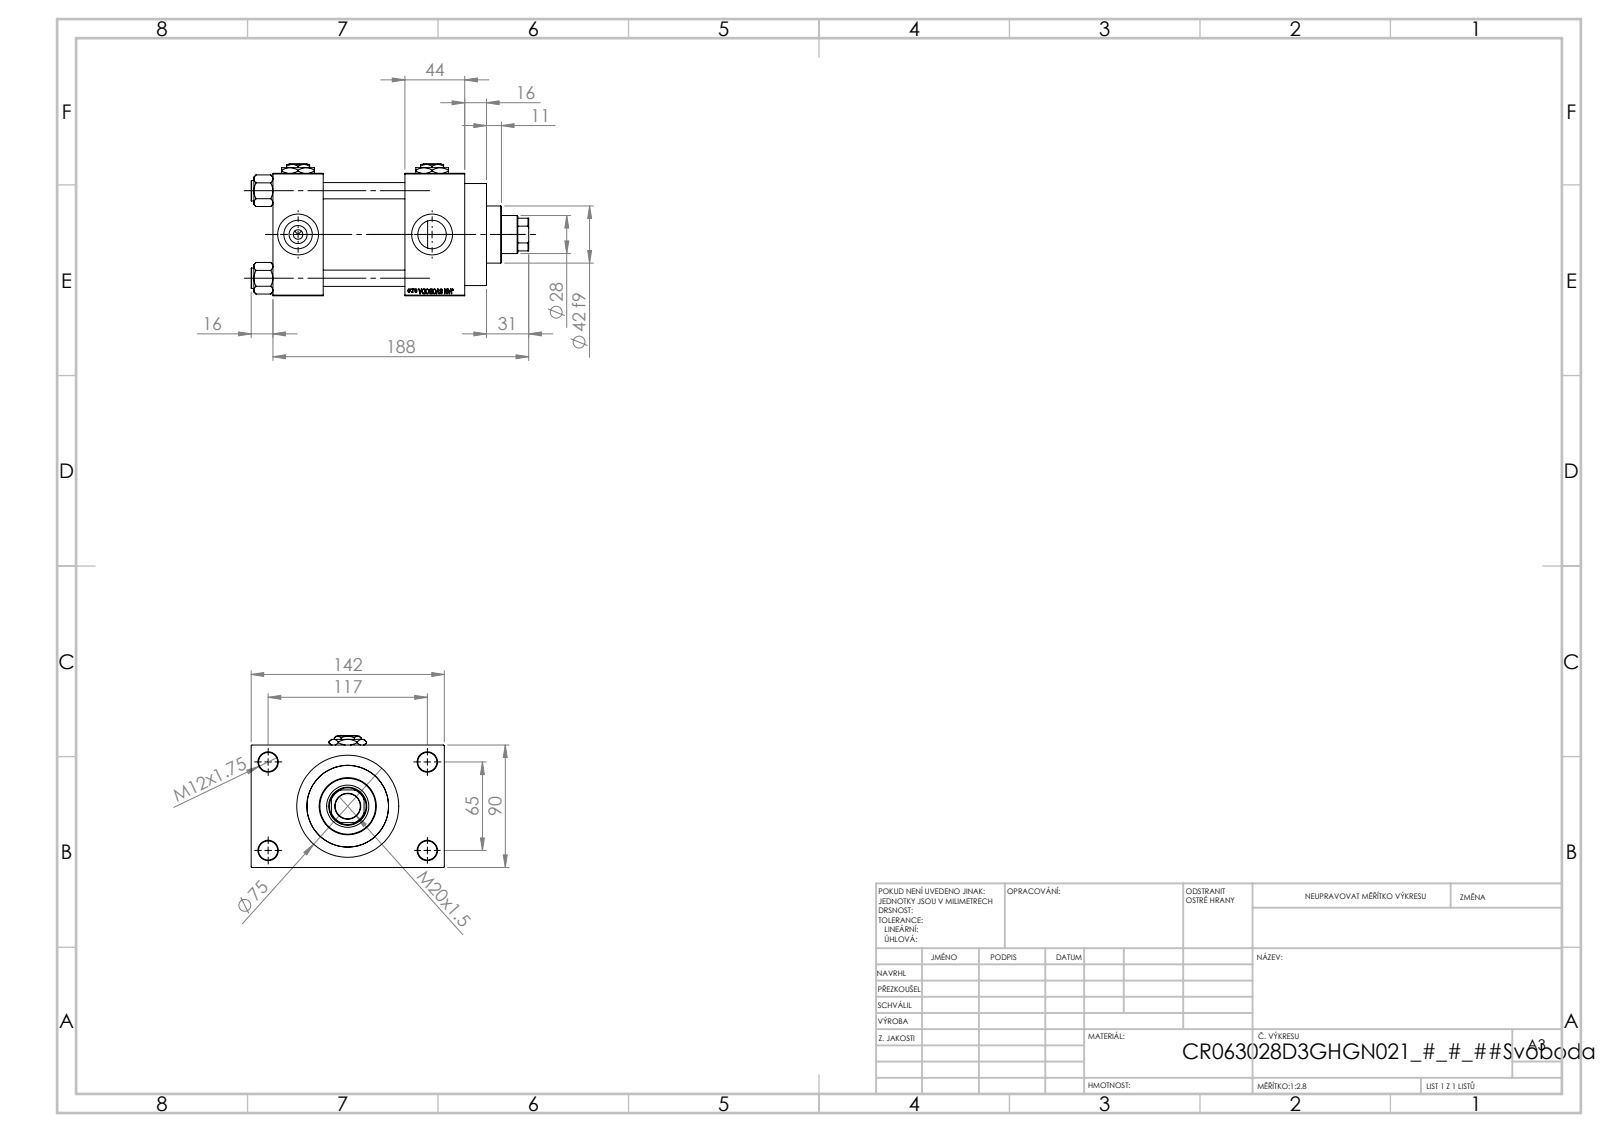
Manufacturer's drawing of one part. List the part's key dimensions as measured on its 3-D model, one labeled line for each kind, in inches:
Part name (STEP PRODUCT): Zatka_pro_OIL_PORT; V215CR_VCP_D; V215CR_D_Body; V215CR_D_TYCINKA (+2 more)
STEP written by: SolidWorks 2019 (CONFIG_CONTROL_DESIGN)
Units: inches
Bodies: 13 solids, 1204 faces (545 planar, 99 cylindrical, 560 other)
Overall size (bounding box): 8.031 × 5.591 × 3.819
Volume: 66.64 in³ · Surface area: 318.7 in²
Round holes (diameter × count): ⌀0.472 ×4, ⌀0.551 ×4, ⌀0.825 ×4, ⌀1.181 ×4, ⌀0.276 ×3, ⌀0.728 ×1, ⌀1.102 ×1, ⌀1.22 ×1, ⌀1.969 ×1, ⌀2.362 ×1, ⌀2.48 ×1
Round bosses / shafts (diameter × count): ⌀0.591 ×4, ⌀2.953 ×1, ⌀2.717 ×1, ⌀1.654 ×1
Partial cylindrical surfaces — rounded edges, fillets, slot ends (radius × count): R0.531 ×1
Main face-to-face distances: 2.362, 3.543, 3.819, 1.457, 4.094, 5.551, 1.732, 1.024, 4.567, 0.63
Hole centre spacings: 1.037, 1.79, 2.531, 2.635, 2.748, 3.569, 4.383, 2.559
